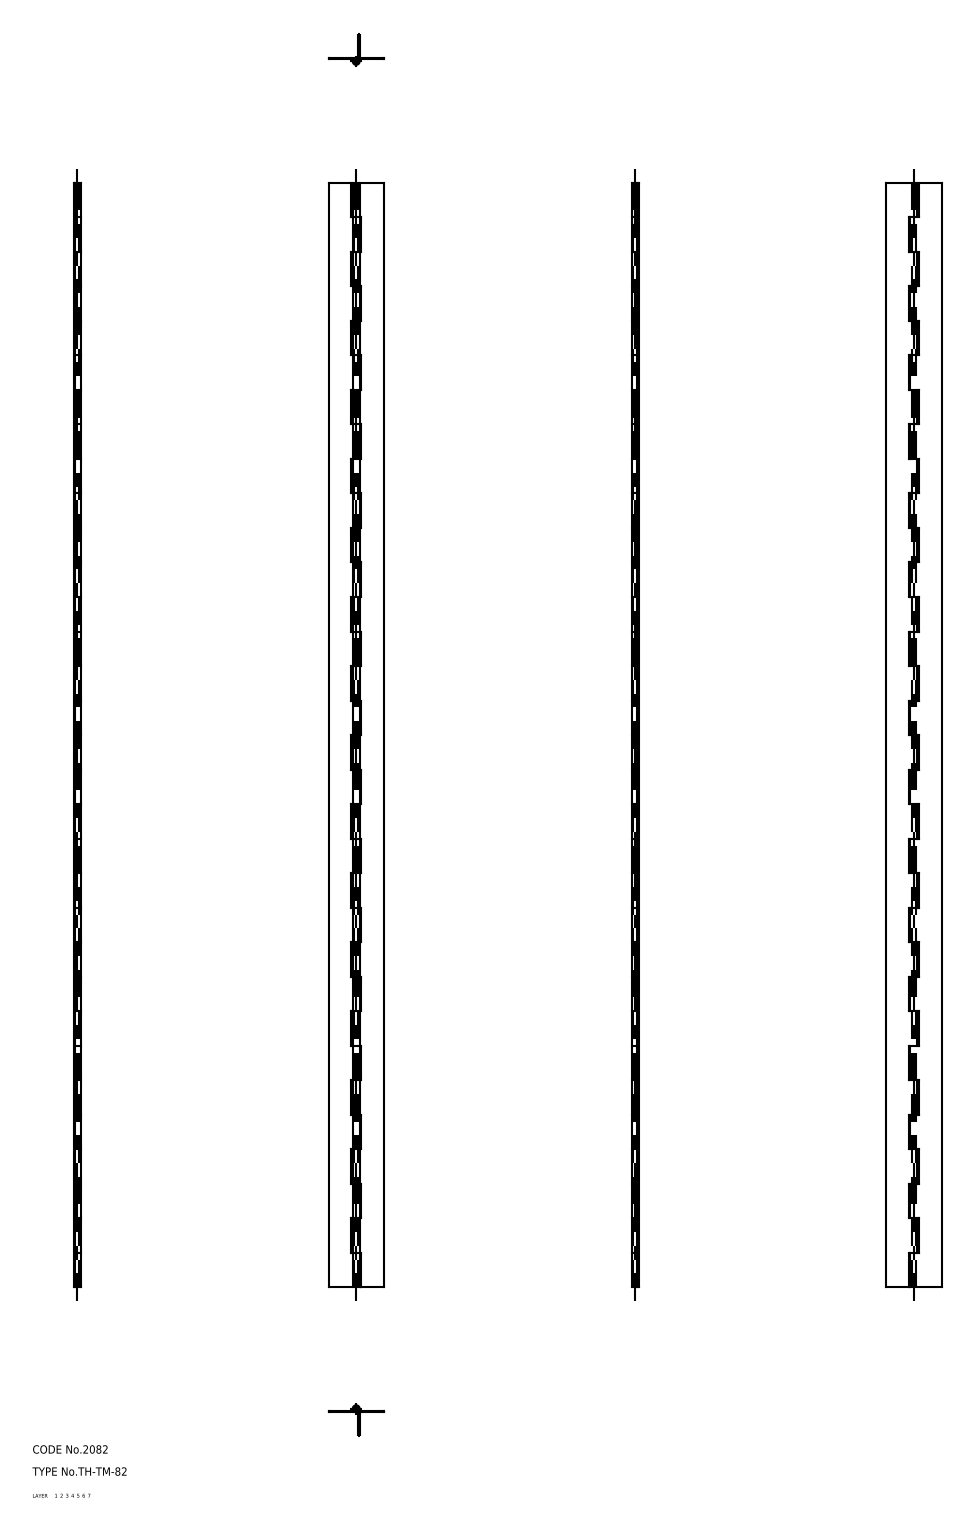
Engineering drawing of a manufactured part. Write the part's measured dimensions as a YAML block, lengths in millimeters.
part_name: "hinge piece_B; hinge piece_A; shaft; TH_TM_82_25863_36"
step_written_by: "CADfix (AUTOMOTIVE_DESIGN)"
units: millimeters
bodies: {solids: 3, faces: 204, planar: 0, cylindrical: 0, other: 204}
overall_size: [400, 20, 2.5]
volume: 5410
surface_area: 21741
